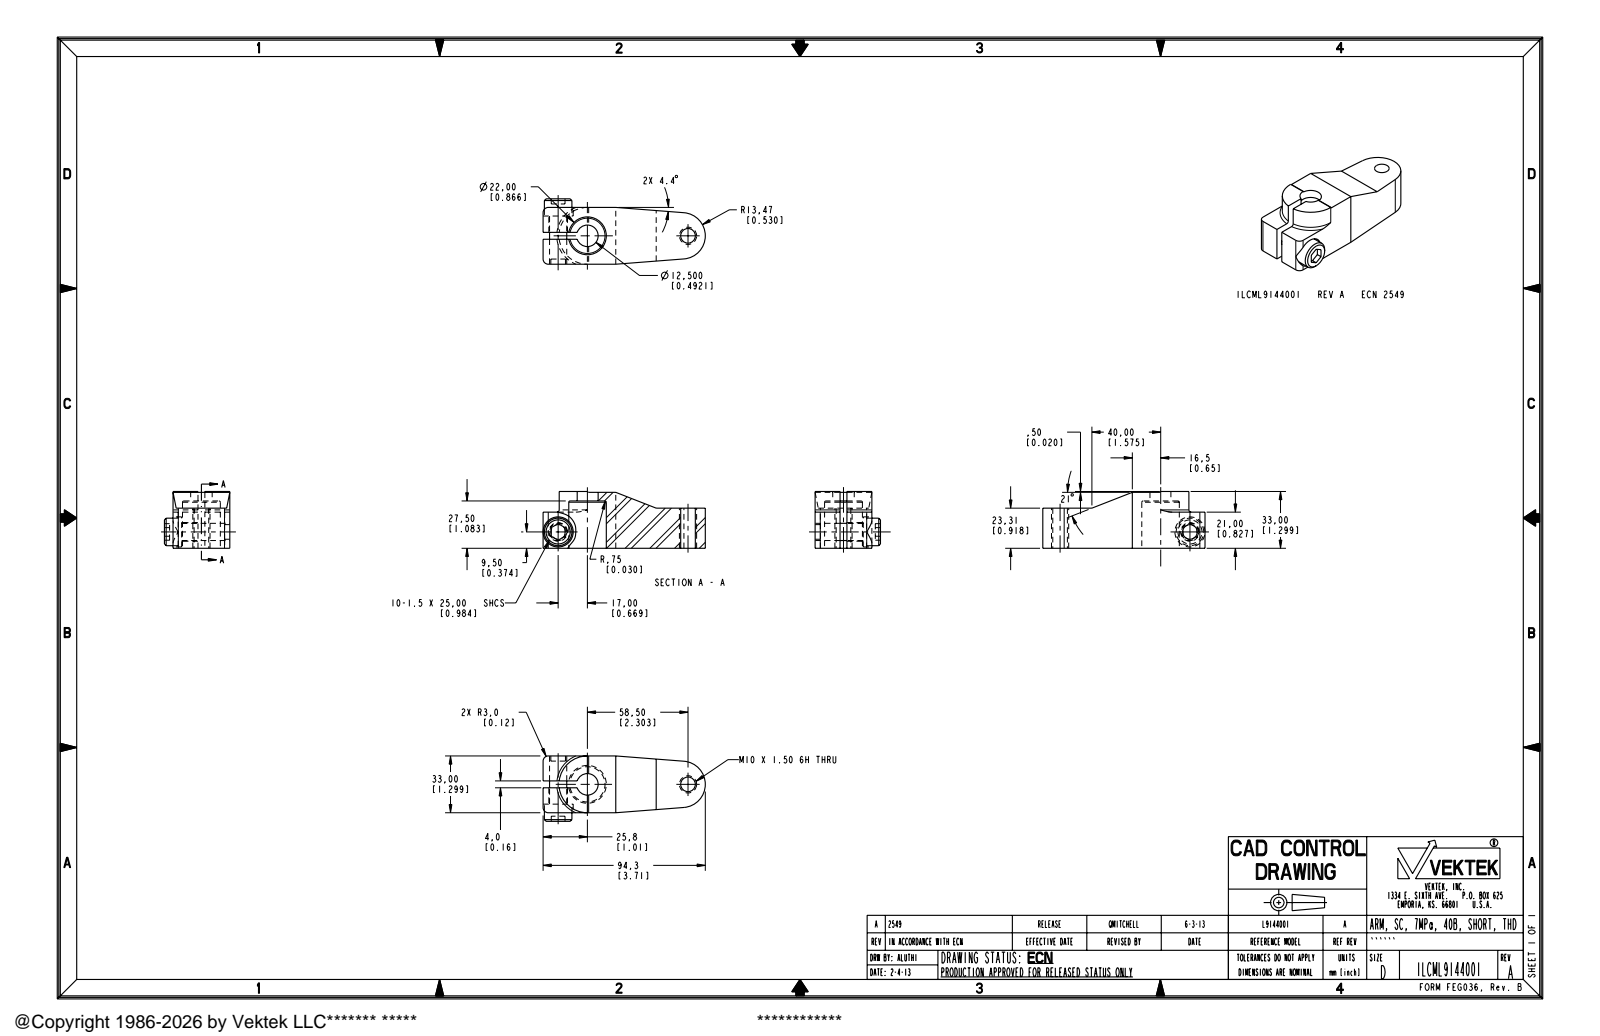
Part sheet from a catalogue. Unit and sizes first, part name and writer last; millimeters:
Units: millimetres
Overall size (bounding box): 94.3 × 38 × 33
Round holes (diameter × count): ⌀8.5 ×2, ⌀10.8 ×1, ⌀12.5 ×1, ⌀17.5 ×1, ⌀22 ×1
Round bosses / shafts (diameter × count): ⌀10 ×2, ⌀16 ×1
Partial cylindrical surfaces — rounded edges, fillets, slot ends (radius × count): R3 ×2, R0.8 ×1, R13.47 ×1, R16.5 ×1
Main face-to-face distances: 33, 23.31, 14.5, 18.5, 32.5, 9.19, 11.5, 5, 21, 2.31
Hole centre spacings: 58.5
Volume: 64 292 mm³ · Surface area: 17 534 mm²
Bodies: 1 solid, 59 faces (28 planar, 26 cylindrical, 5 other)
Part name (STEP PRODUCT): ILCML9144001
STEP written by: PRO/ENGINEER BY PARAMETRIC TECHNOLOGY CORPORATION, 2007460 (AUTOMOTIVE_DESIGN_CC2)
